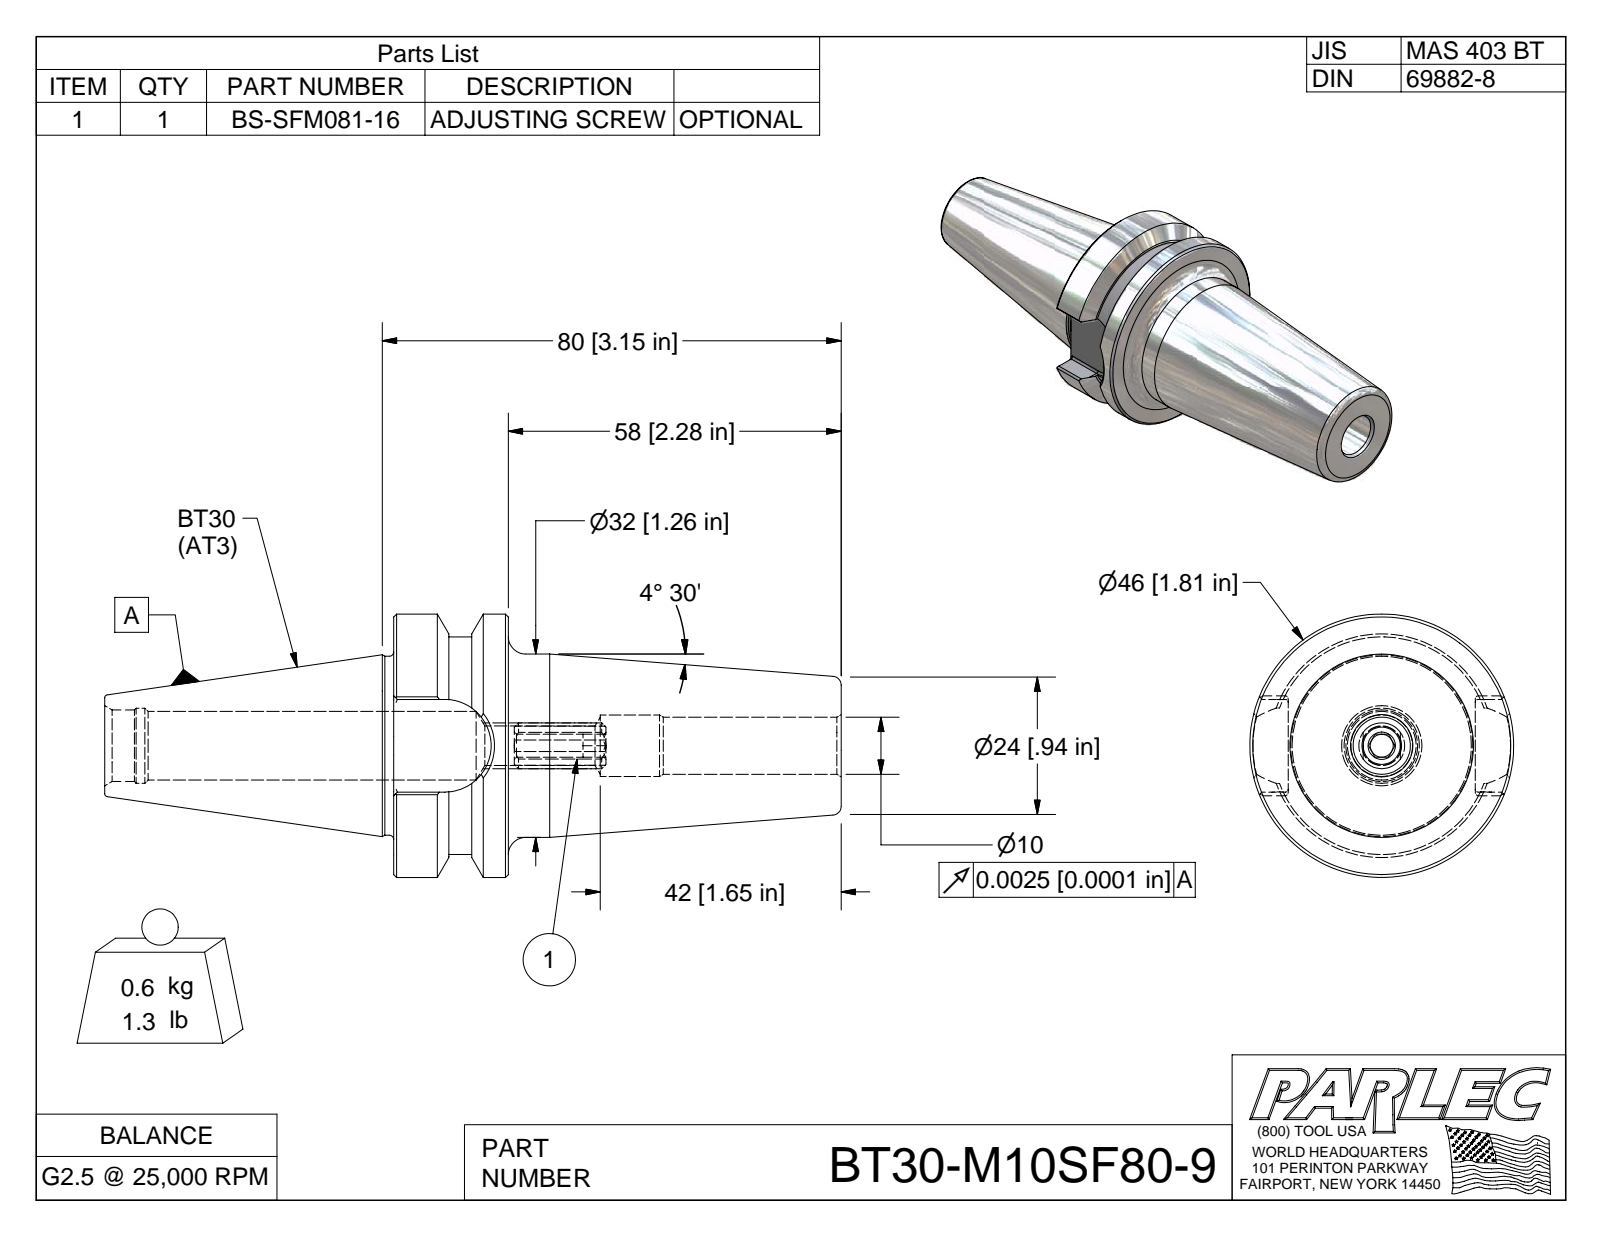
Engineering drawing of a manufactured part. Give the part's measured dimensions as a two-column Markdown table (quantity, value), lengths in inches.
| quantity | value |
| --- | --- |
| part name | BT30-M10SF80-9; BT30-M10SF80-9-1; BS-SFM081-16 |
| STEP written by | Autodesk Inventor 2009 (AUTOMOTIVE_DESIGN) |
| units | inches |
| bodies | 2 solids, 92 faces (35 planar, 22 cylindrical, 35 other) |
| overall size | 5.056 × 1.811 × 1.811 |
| volume | 4.84 in³ |
| surface area | 30.29 in² |
| round holes (diameter × count) | 0.393 × 1, 0.423 × 1, 0.517 × 1 |
| round bosses / shafts (diameter × count) | 1.811 × 1, 1.26 × 1, 1.23 × 1 |
| partial cylindrical surfaces (radius × count) | 0.02 × 8, 0.157 × 1, 0.319 × 1, 0.748 × 1 |
| main face-to-face distances | 0.787, 3.072, 2.285, 1.283, 0.514, 0.77, 0.157, 0.256, 1.984, 2.771 |
